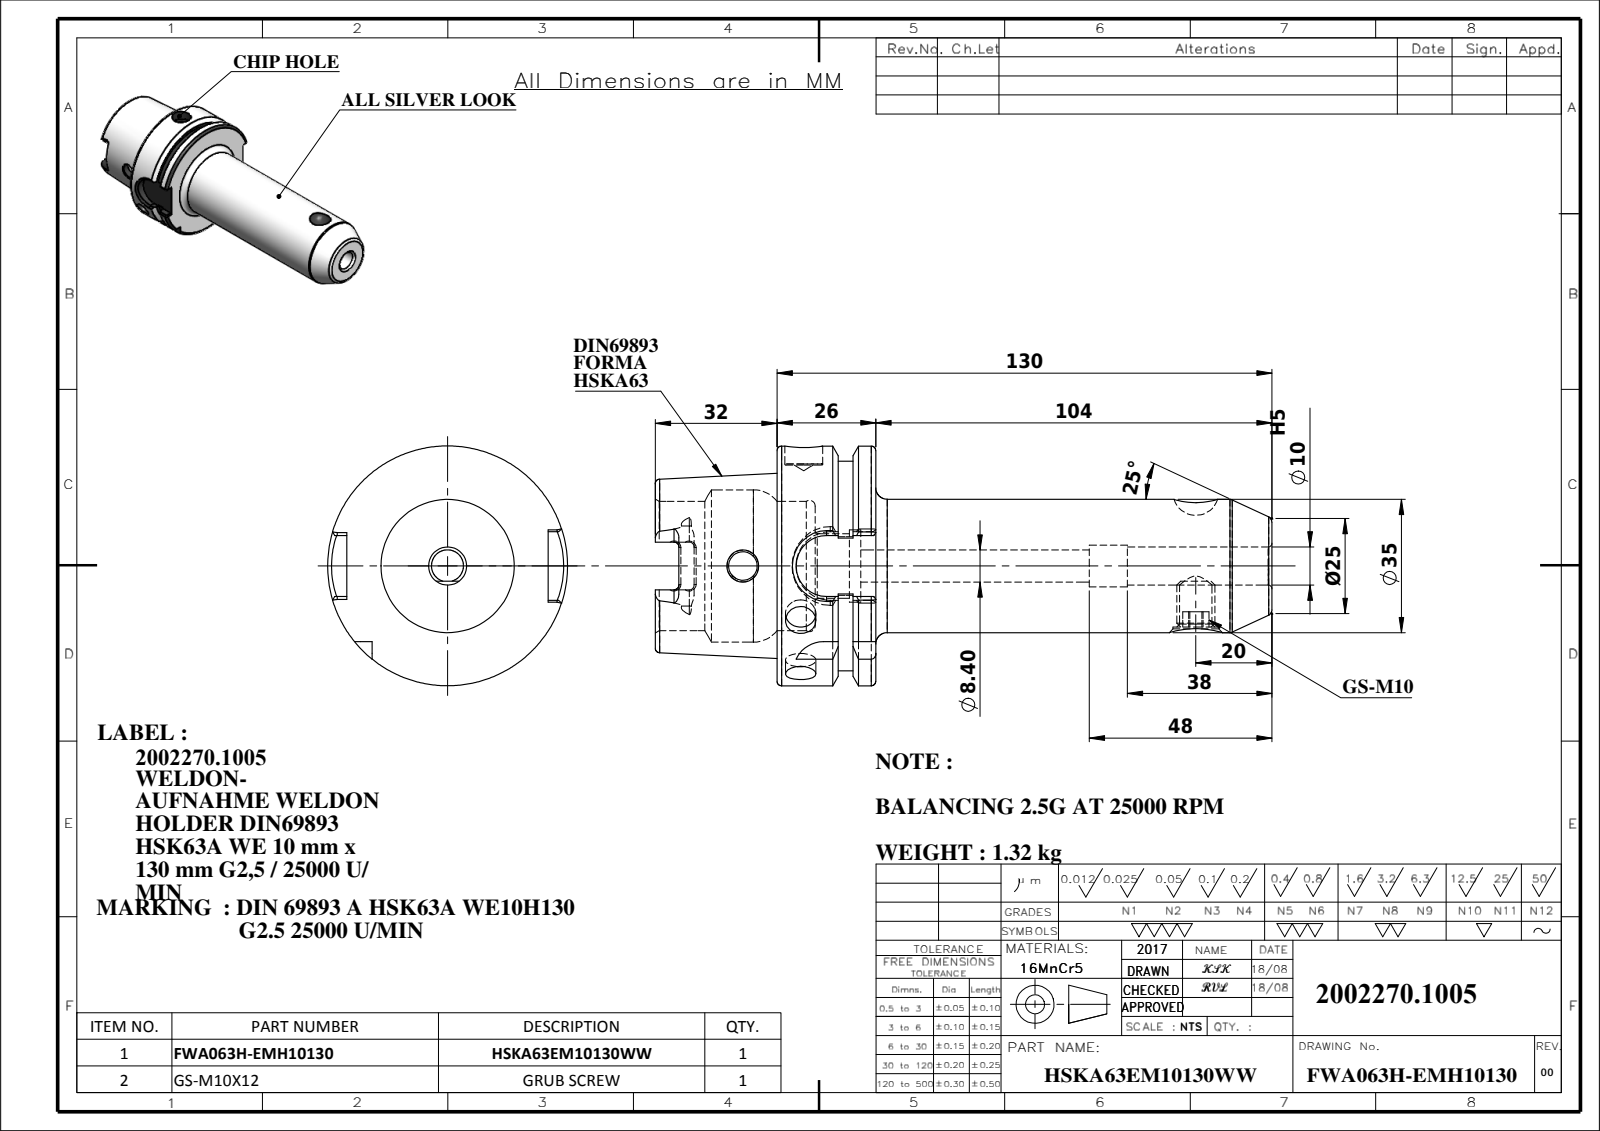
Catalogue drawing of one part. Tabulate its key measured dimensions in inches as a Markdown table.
| quantity | value |
| --- | --- |
| part name | HSKA63EM10130WW; GS-M10X12-DIN1835-B; 9163A-WE810130 |
| STEP written by | SolidWorks 2018 (CONFIG_CONTROL_DESIGN) |
| units | inches |
| bodies | 2 solids, 194 faces (61 planar, 57 cylindrical, 76 other) |
| overall size | 6.378 × 2.48 × 2.48 |
| volume | 10.44 in³ |
| surface area | 57.29 in² |
| round holes (diameter × count) | 0.315 × 2, 0.394 × 2, 0.295 × 1, 0.331 × 1, 0.335 × 1, 0.433 × 1, 0.472 × 1, 0.669 × 1, 0.748 × 1, 1.339 × 1, 1.575 × 1 |
| round bosses / shafts (diameter × count) | 2.48 × 1, 2.165 × 1, 1.378 × 1, 0.394 × 1 |
| partial cylindrical surfaces (radius × count) | 0.051 × 6, 0.113 × 4, 0.315 × 2, 0.354 × 1 |
| main face-to-face distances | 1.022, 0.394, 0.628, 1.26, 1.654, 2.281, 6.378, 5.118, 4.724, 4.096 |
| hole center spacings | 4.055 |
